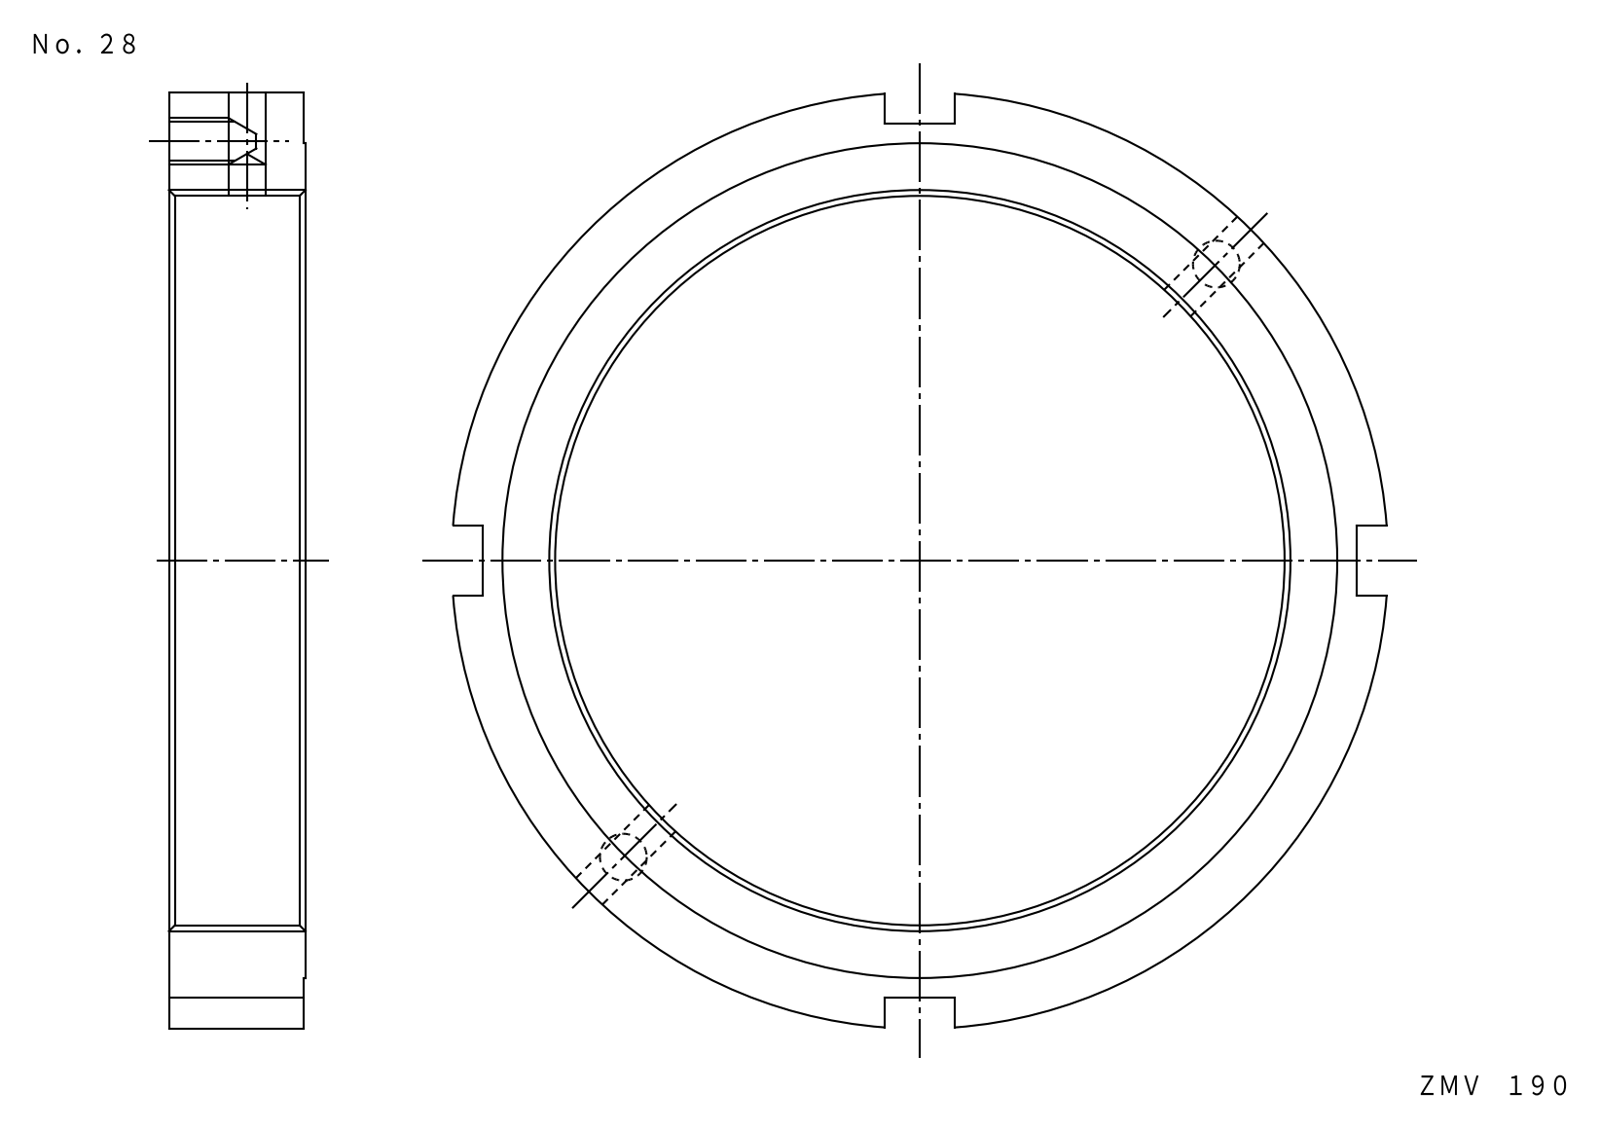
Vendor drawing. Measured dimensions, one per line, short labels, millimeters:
name: FKD ZMV190
written by: Autodesk Inventor LT (CONFIG_CONTROL_DESIGN)
unit: mm
bodies: 1 solid, 29 faces (15 planar, 10 cylindrical, 4 other)
size: 239.32 × 239.32 × 35
volume: 558 791 mm³; area: 83 914 mm²
holes: 2× ⌀9.6, 2× ⌀10.11, 1× ⌀190
bosses: 1× ⌀240, 1× ⌀203
face distances: 34.5, 0.5, 35, 103, 121, 224, 18
hole spacings: 102.5, 205
